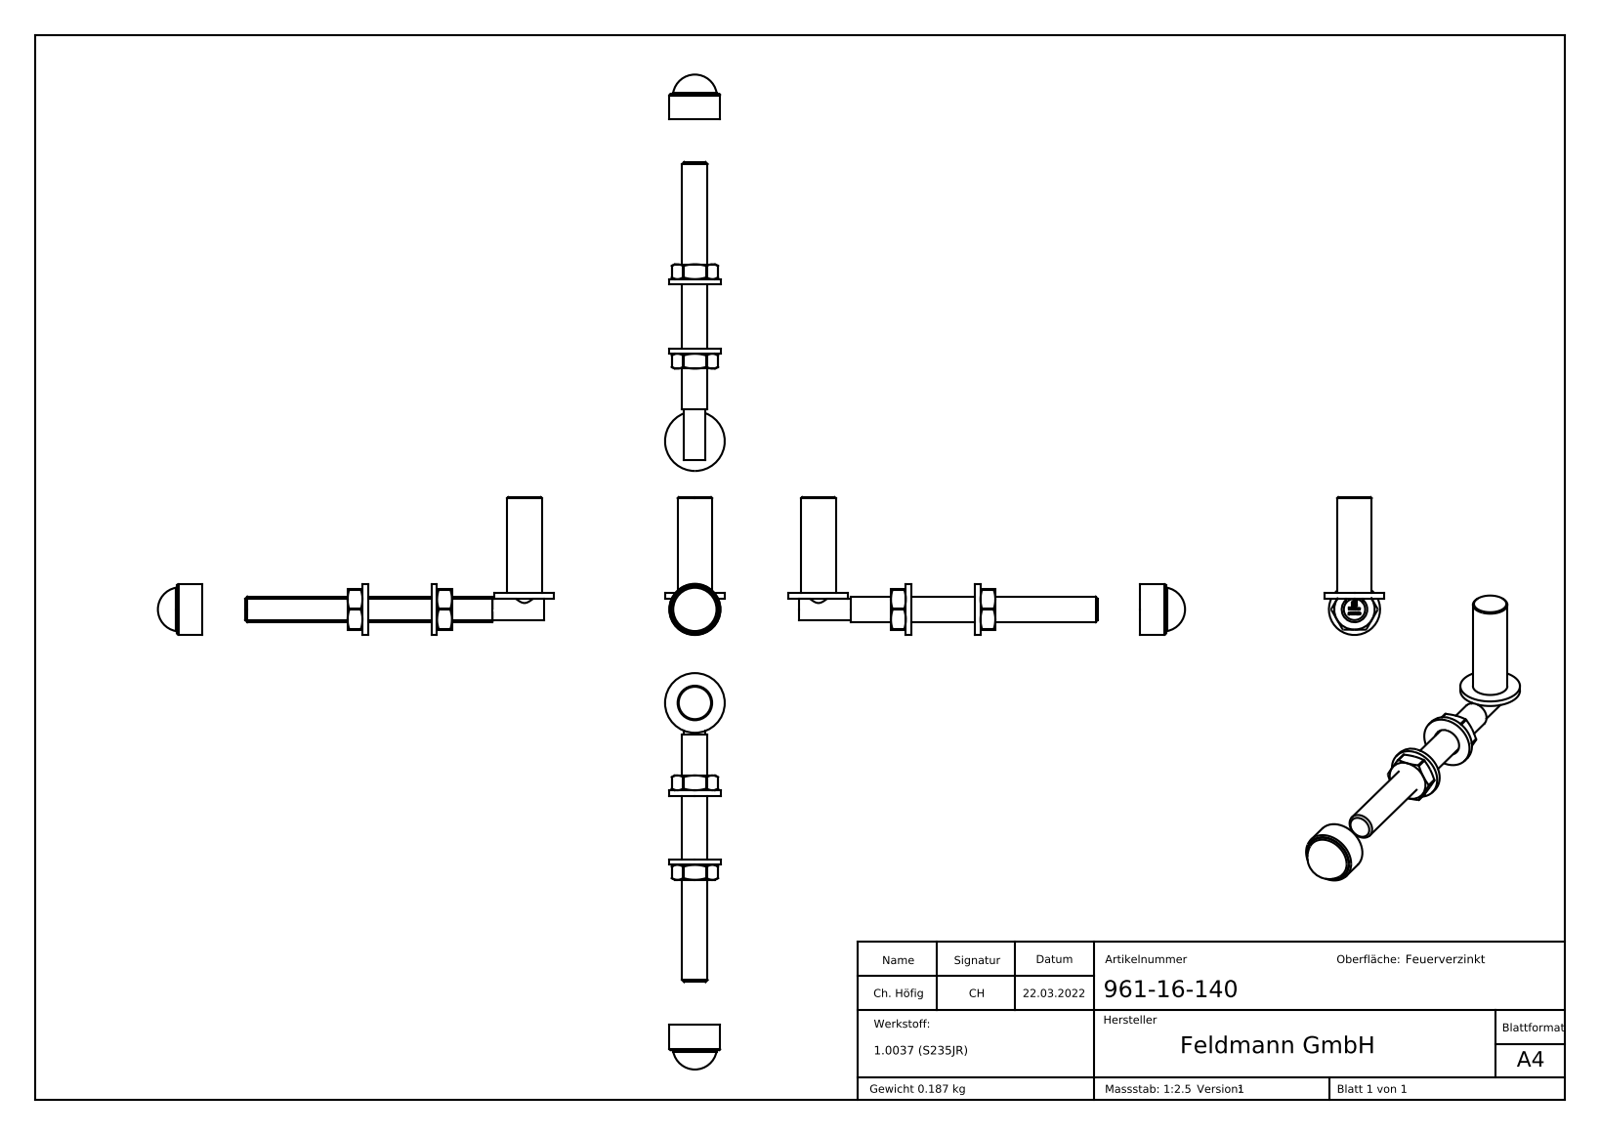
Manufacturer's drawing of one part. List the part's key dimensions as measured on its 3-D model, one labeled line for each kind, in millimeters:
Part name (STEP PRODUCT): 961-16-140; 961-1X-XXX Teil2_961-XX-XXX Teil2; 961-1X-XXX Teil1_961-16-140 Teil1; DIN 936 M8-M24_DIN 936 M12 (+1 more)
STEP written by: SolidWorks 2018 (CONFIG_CONTROL_DESIGN)
Units: millimetres
Bodies: 6 solids, 354 faces (191 planar, 25 cylindrical, 138 other)
Overall size (bounding box): 186 × 64.7 × 28
Volume: 32 646 mm³ · Surface area: 16 041 mm²
Round holes (diameter × count): ⌀10.2 ×1, ⌀13 ×1, ⌀19 ×1
Round bosses / shafts (diameter × count): ⌀28 ×1, ⌀24 ×1, ⌀23.8 ×1, ⌀16.2 ×1, ⌀12 ×1, ⌀10 ×1, ⌀8 ×1
Partial cylindrical surfaces — rounded edges, fillets, slot ends (radius × count): R0.5 ×6
Main face-to-face distances: 2.5, 19, 32.5, 35, 9.5, 7, 39.5, 42, 30, 1.8
